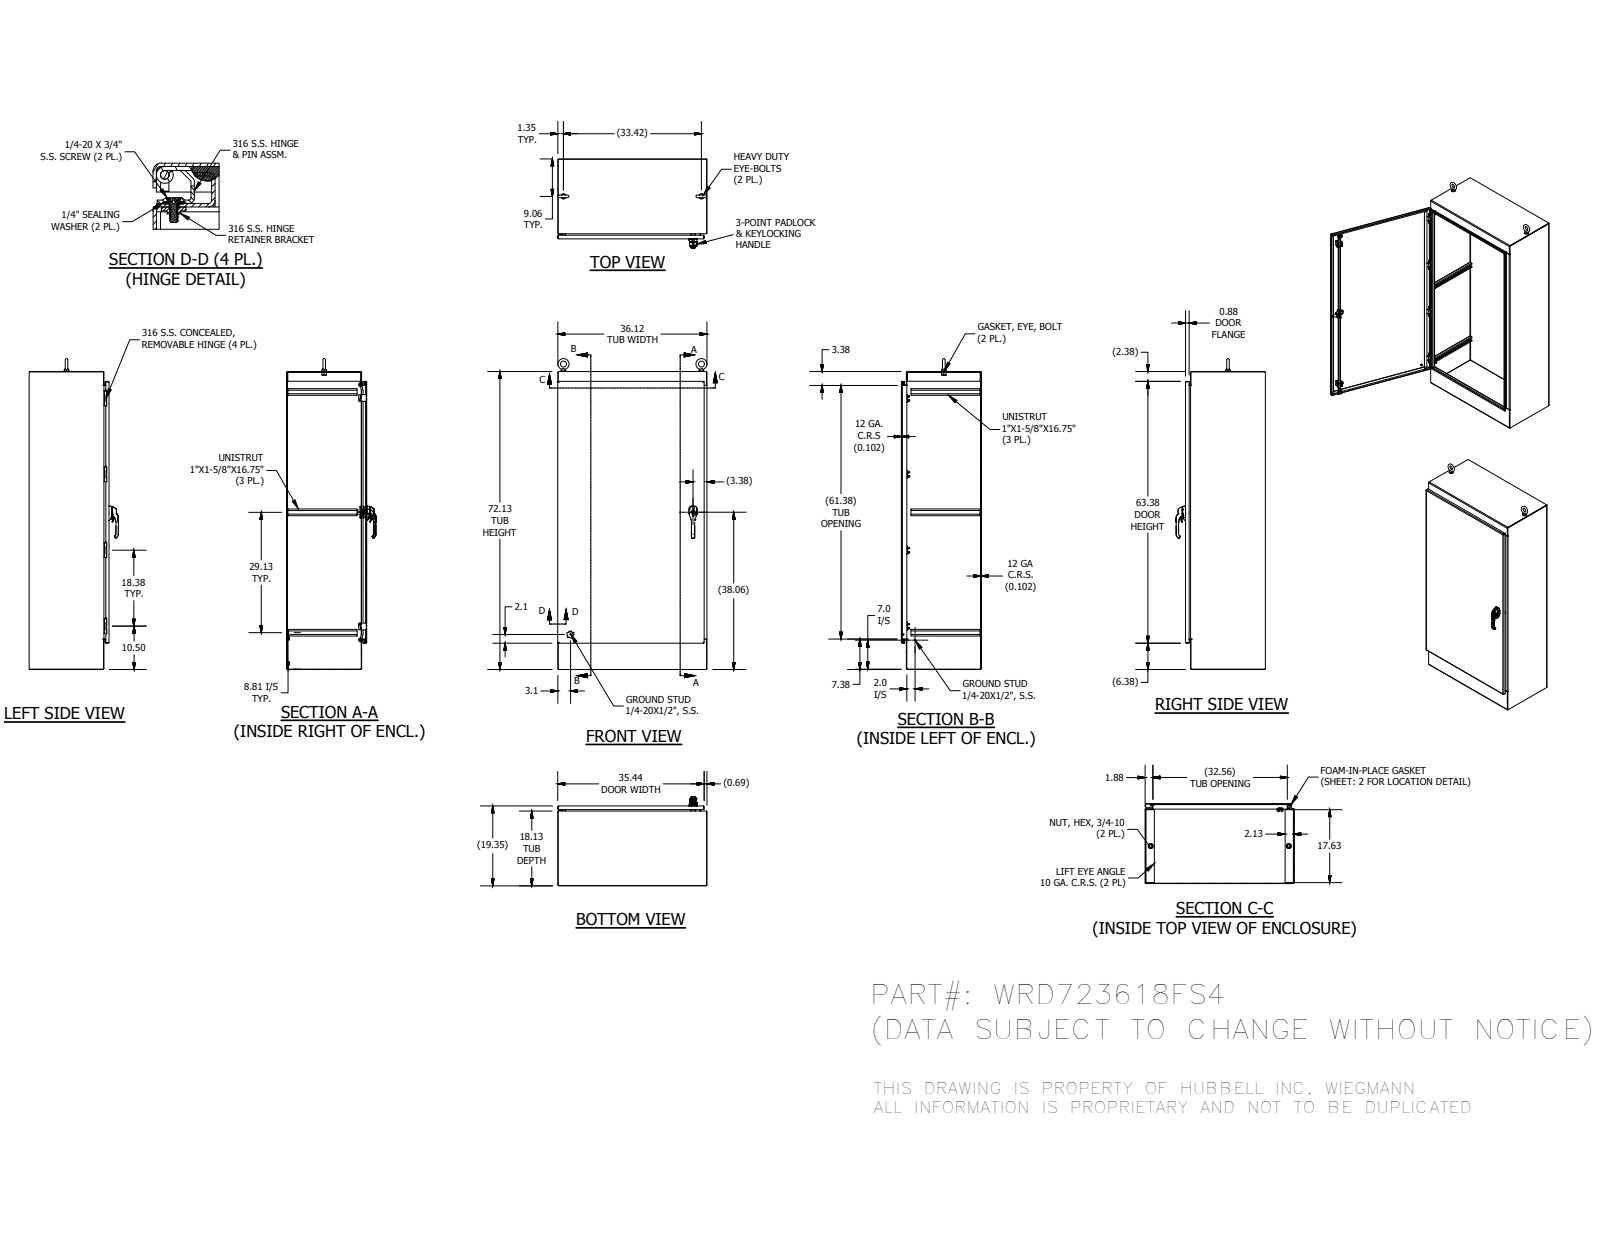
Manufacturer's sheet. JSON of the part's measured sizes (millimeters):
{"part_name": "WRD723618FS4BLR; WRD3618FS4TOP; WRD3618FS4BTM; WRD7236FS4DR (+8 more)", "step_written_by": "Autodesk Inventor 2016 (AUTOMOTIVE_DESIGN)", "units": "millimeters", "bodies": {"solids": 85, "faces": 3586, "planar": 1457, "cylindrical": 1207, "other": 922}, "overall_size": [1911.29, 917.63, 549.04], "volume_mm3": 18620000, "surface_area_mm2": 14000000, "round_holes": [[5.84, 8], [7.02, 8], [7.14, 8], [16.51, 8], [5.08, 4], [5.4, 3], [6, 3], [7.11, 3], [6.13, 2], [6.35, 2], [6.41, 2], [10.16, 2]], "round_bosses_or_shafts": [[6.35, 15], [15.88, 8], [10.25, 8], [4.63, 8], [31.75, 2], [28.45, 2], [25.4, 2], [19.05, 2]], "partial_cylinders_radius": [[0.5, 164], [0.3, 86], [1.59, 27], [0.25, 24], [3.17, 20], [0.47, 19], [2, 15], [1.27, 14]], "face_to_face_distances": [2.59, 488.83, 914.99, 486.24, 491.42, 912.4, 1829.39, 917.58, 457.79, 31.04], "hole_center_spacings": [12.5, 25.4, 466.73, 933.45, 6.5, 22.5, 51.5, 6]}
